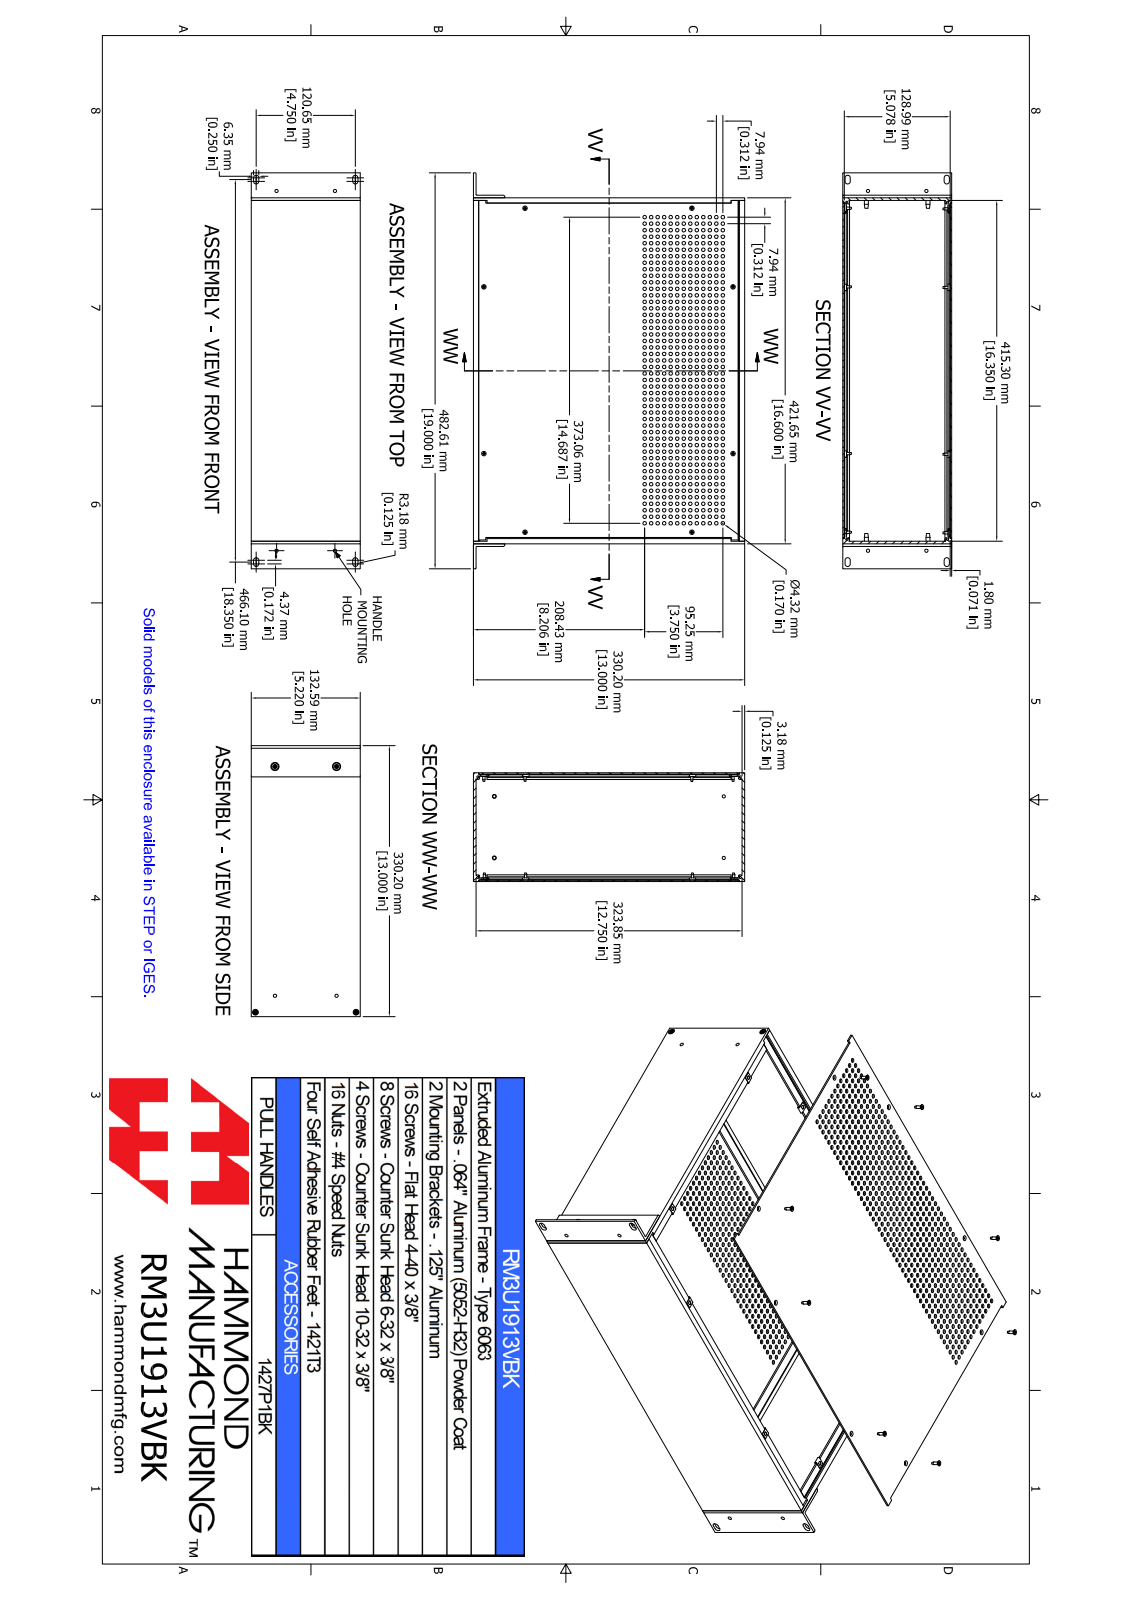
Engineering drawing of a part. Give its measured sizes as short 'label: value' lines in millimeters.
name: RM3U1913VBK
written by: SolidWorks 2021 (AUTOMOTIVE_DESIGN)
unit: mm
bodies: 52 solids, 2600 faces (636 planar, 1468 cylindrical, 496 other)
size: 482.6 × 330.2 × 132.6
volume: 1 240 000 mm³; area: 1 067 000 mm²
holes: 624× ⌀4.3, 8× ⌀2.5, 8× ⌀3, 8× ⌀4, 8× ⌀4.3, 4× ⌀3.5, 4× ⌀4, 4× ⌀4, 2× ⌀5
bosses: 16× ⌀5.4, 16× ⌀2.8, 4× ⌀6, 4× ⌀3.5, 2× ⌀8.5, 2× ⌀4.8
rounds: 21× R1, 16× R3.2, 15× R1.2, 8× R0.9, 8× R1.3, 4× R1, 2× R2
face distances: 1.8, 130.8, 132.6, 129, 3.2, 3.2, 421.6, 330.2, 323.9, 327
hole spacings: 8, 31.8, 23.8, 1.1, 203.2, 270.8, 39.7, 15.9
